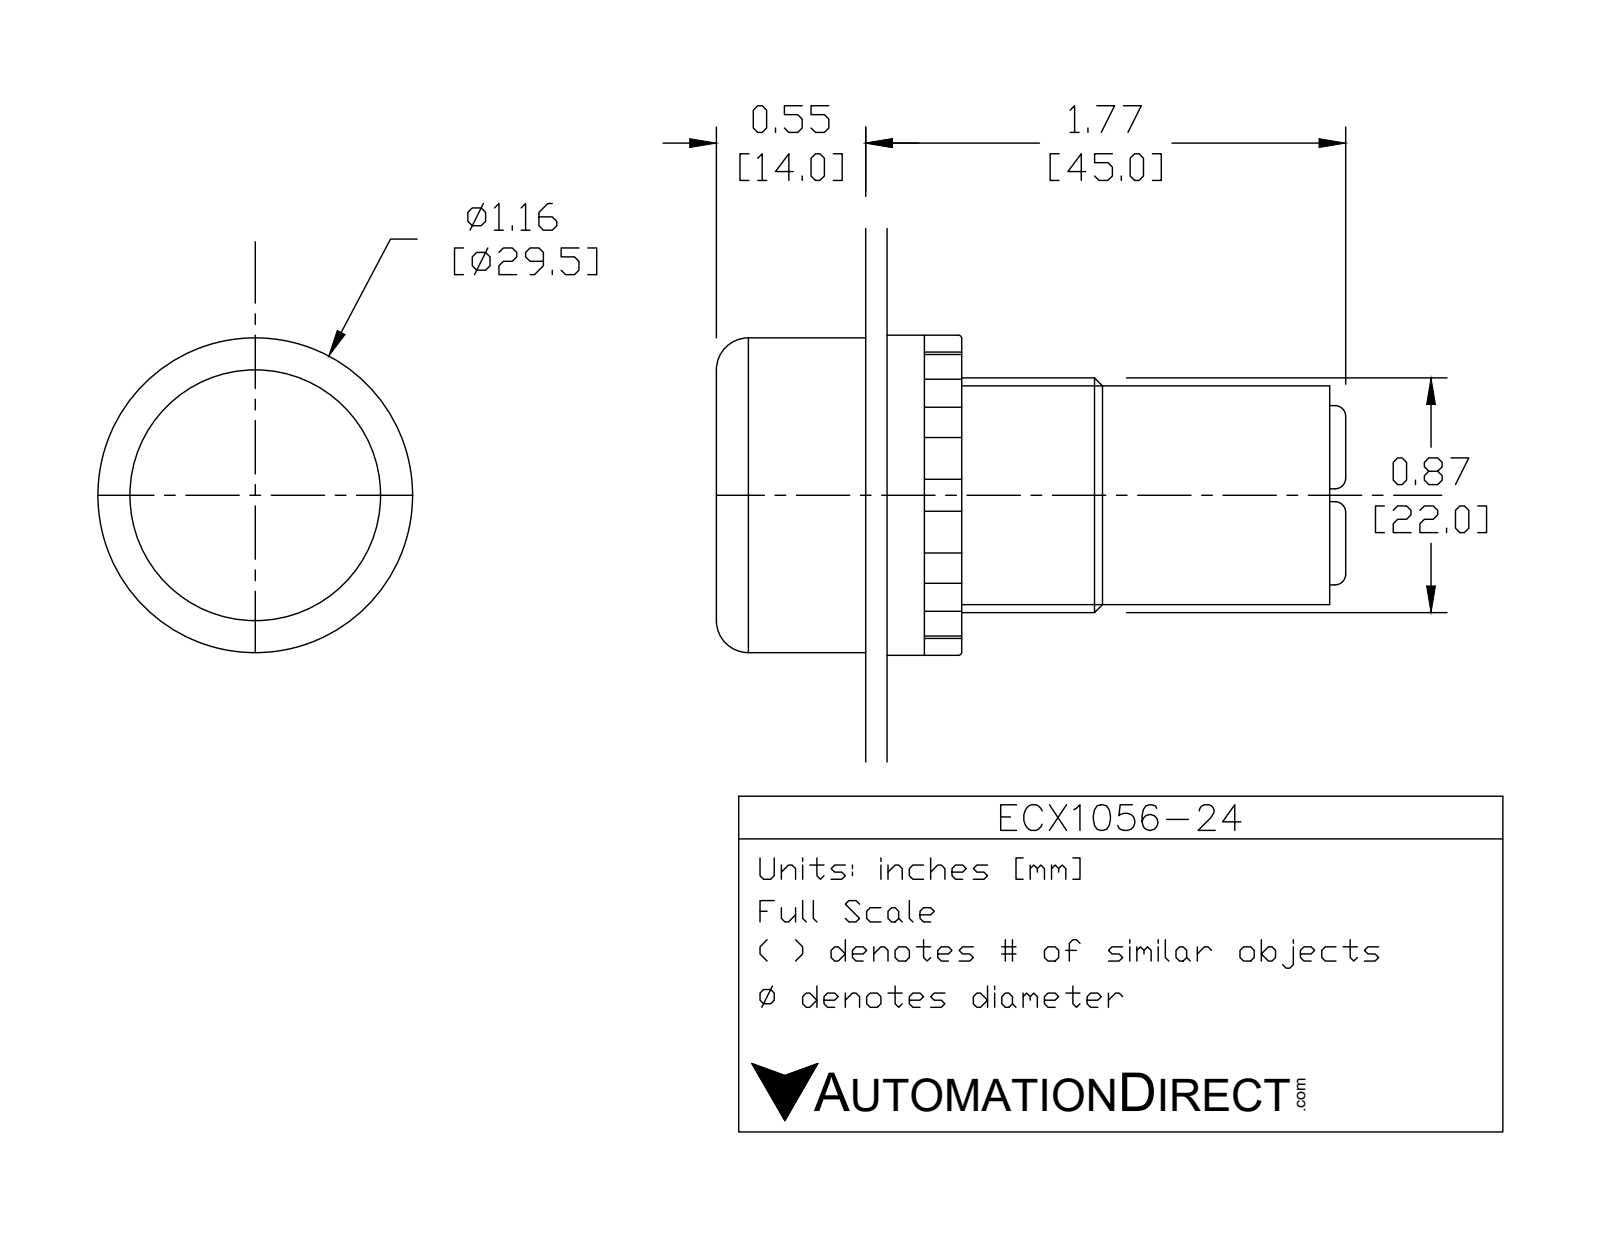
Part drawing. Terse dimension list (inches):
name: ECX1056-24
written by: SolidWorks 2017 (AUTOMOTIVE_DESIGN)
unit: in
bodies: 6 solids, 125 faces (63 planar, 41 cylindrical, 21 other)
size: 2.323 × 1.181 × 1.181
volume: 1.605 in³; area: 15.04 in²
holes: 2× ⌀0.217, 1× ⌀0.886
bosses: 2× ⌀0.157, 1× ⌀1.181, 1× ⌀1.142, 1× ⌀1.043, 1× ⌀0.866, 1× ⌀0.787
rounds: 12× R0.039, 1× R0.354
face distances: 0.531, 0.02, 0.551, 0.787, 0.236, 0.256, 1.535, 0.276, 0.512, 1.063
hole spacings: 0.182, 0.364
